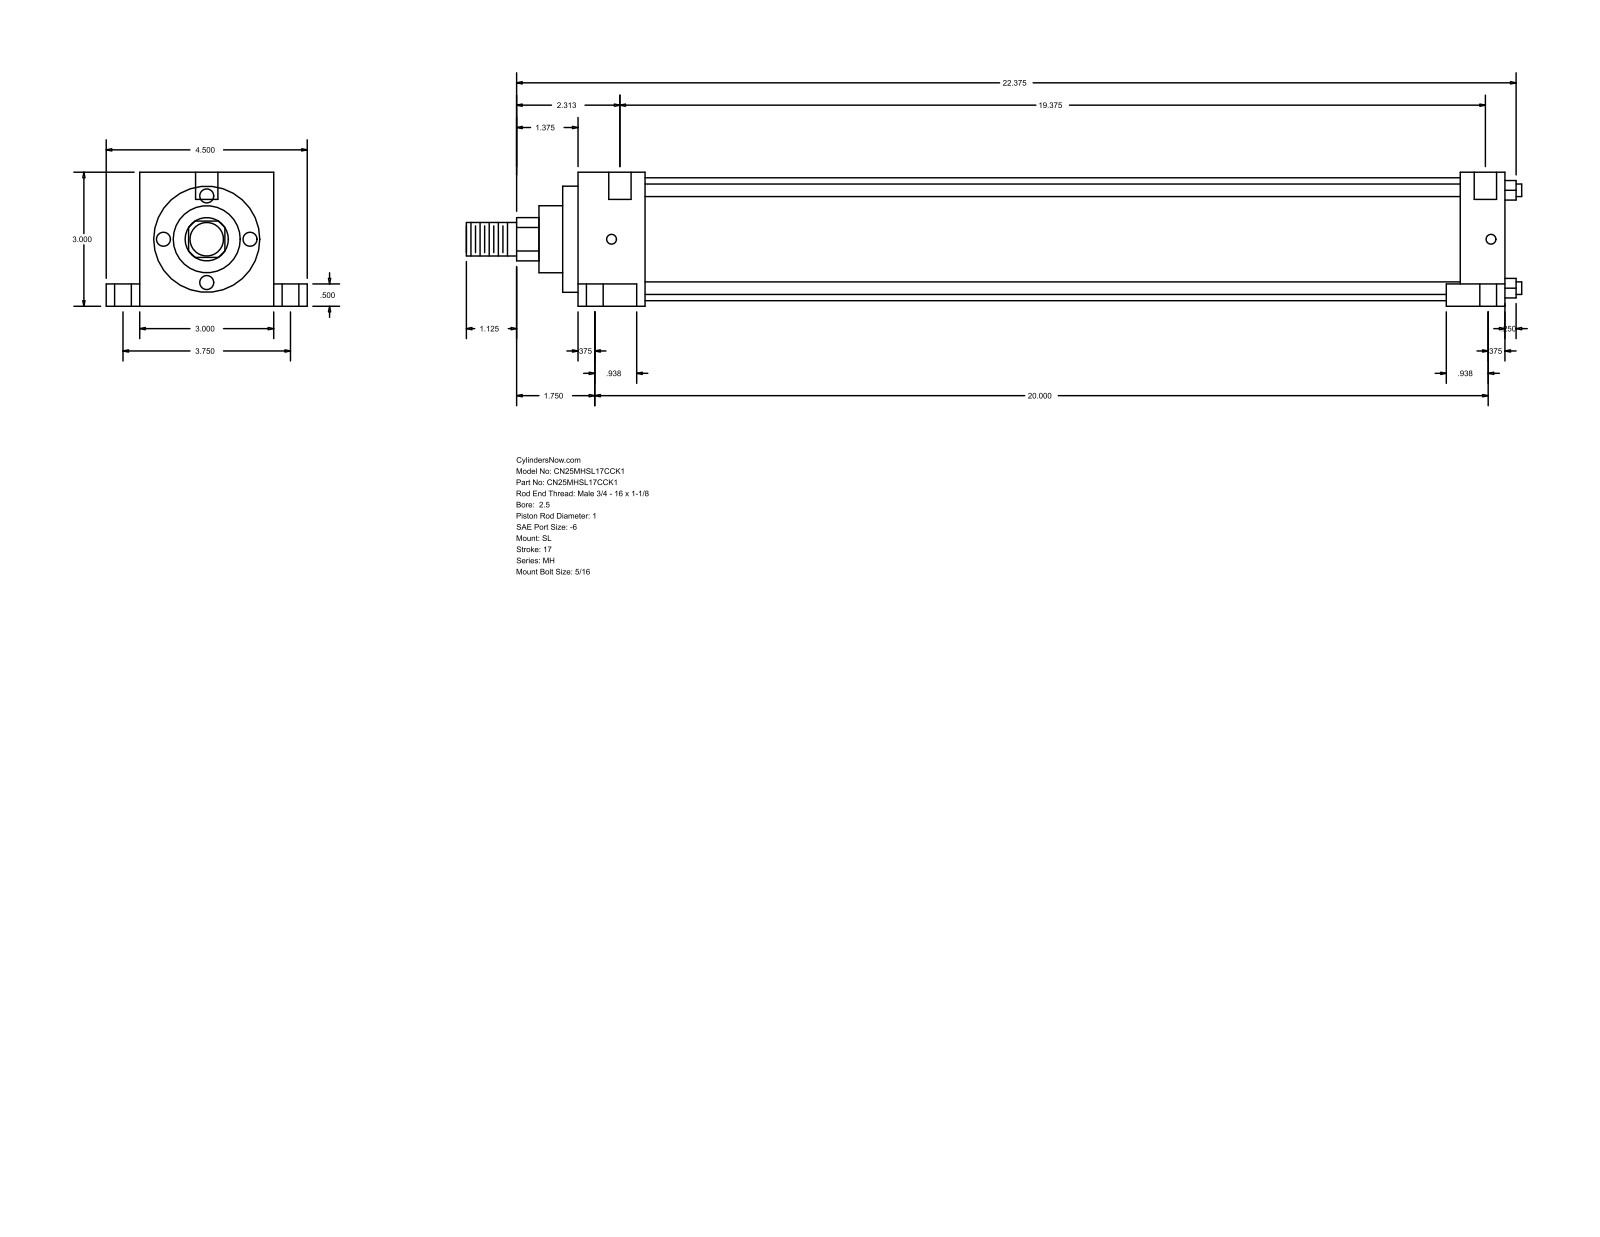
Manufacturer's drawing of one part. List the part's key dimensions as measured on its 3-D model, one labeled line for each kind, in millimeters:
Part name (STEP PRODUCT): MH_SL__0250_1
STEP written by: GSSL Pune (CONFIG_CONTROL_DESIGN)
Units: millimetres
Bodies: 0 solids, 86 faces (61 planar, 25 cylindrical, 0 other)
Overall size (bounding box): 600.08 × 114.3 × 76.2
Round holes (diameter × count): ⌀5.56 ×2, ⌀9.53 ×2, ⌀15.88 ×2, ⌀12.7 ×1
Round bosses / shafts (diameter × count): ⌀7.14 ×4, ⌀69.85 ×1, ⌀60.33 ×1, ⌀38.1 ×1, ⌀25.4 ×1, ⌀19.05 ×1
Partial cylindrical surfaces — rounded edges, fillets, slot ends (radius × count): R12.29 ×1
Main face-to-face distances: 76.2, 25.4, 510.39, 535.79, 12.7, 63.5, 19.05, 95.25, 13.49, 523.88
Hole centre spacings: 47.65, 3.18, 95.24
